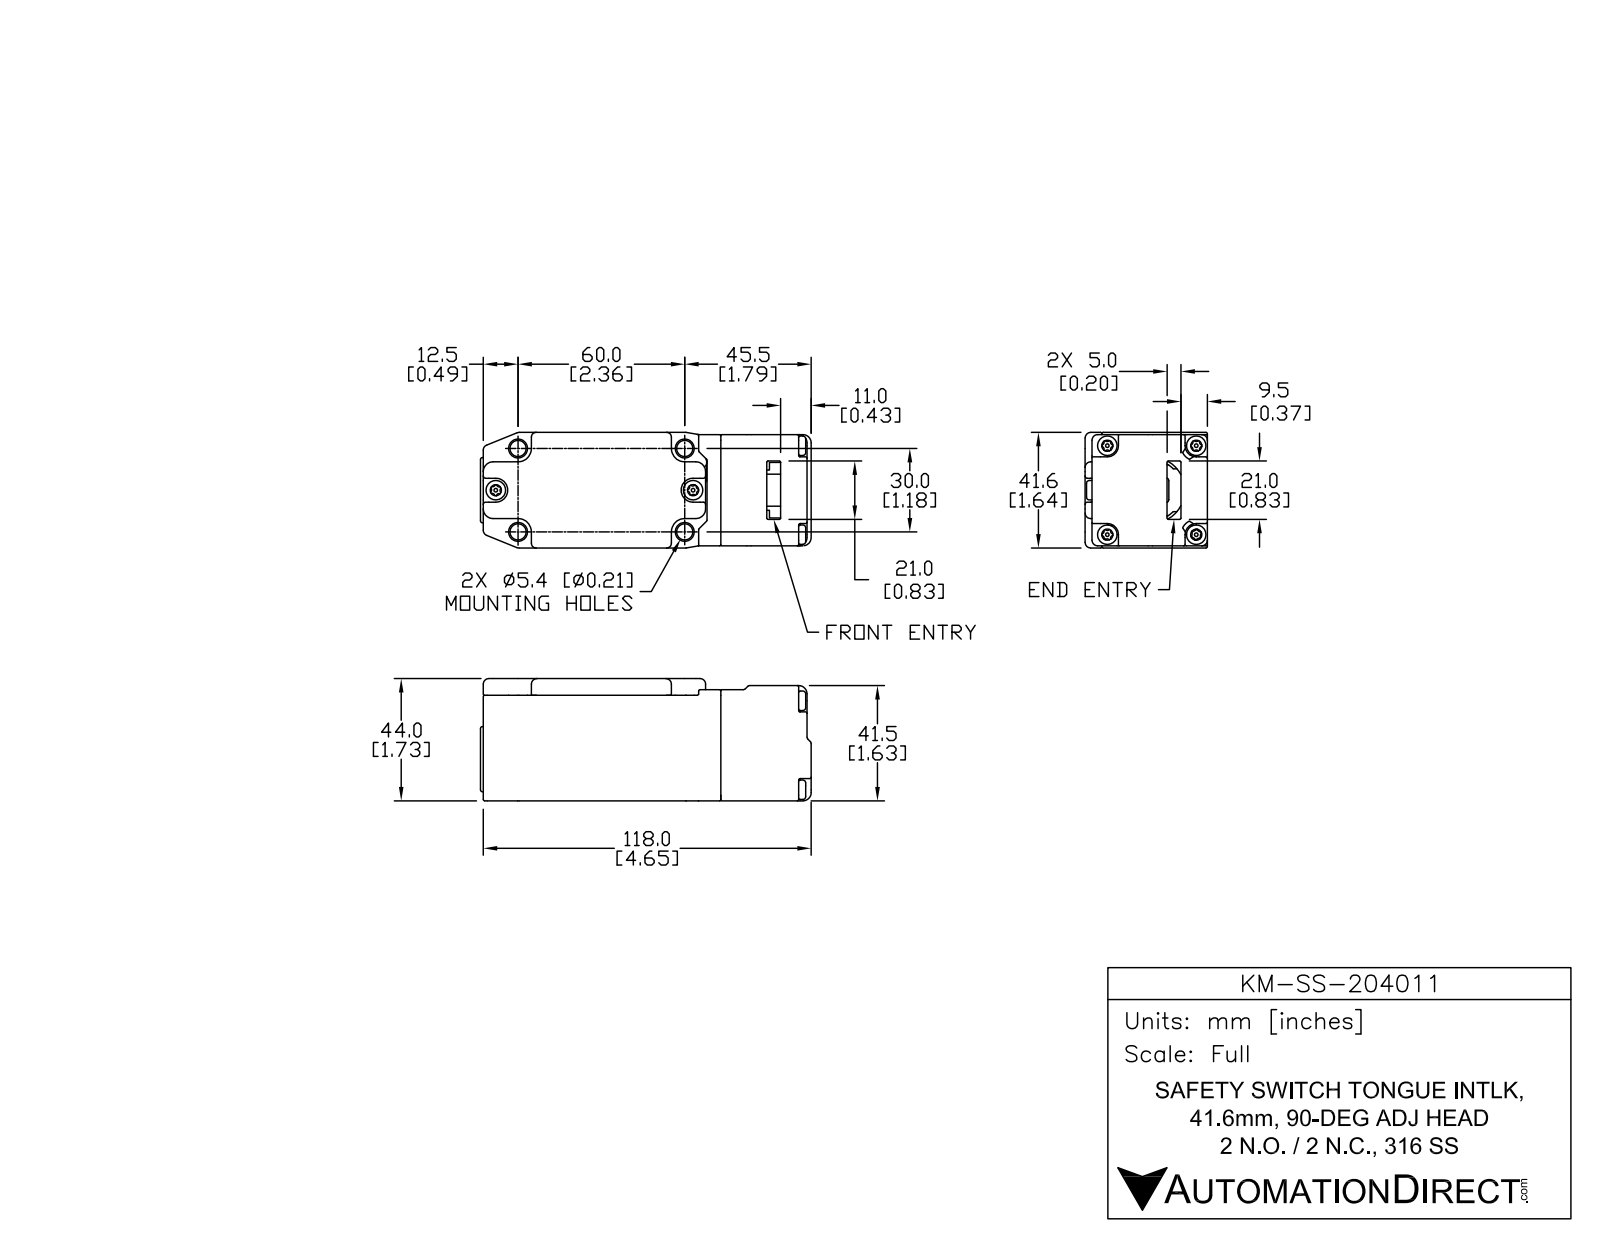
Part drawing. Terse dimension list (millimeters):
name: KM-SS-204011
written by: SolidWorks 2013 (AUTOMOTIVE_DESIGN)
unit: mm
bodies: 1 solid, 632 faces (120 planar, 278 cylindrical, 234 other)
size: 119.63 × 44.06 × 41.6
volume: 190 045 mm³; area: 28 649 mm²
holes: 4× ⌀5.4
bosses: 4× ⌀5.5, 2× ⌀6.63, 1× ⌀23, 1× ⌀5.6
rounds: 134× R0.25, 43× R0.5, 6× R5, 5× R3, 4× R1, 4× R1.7, 2× R2.25, 2× R2.5
face distances: 41.6, 0.8, 40.8, 44, 40, 0.5, 43.5, 5, 118, 2.6
hole spacings: 32, 60, 68
